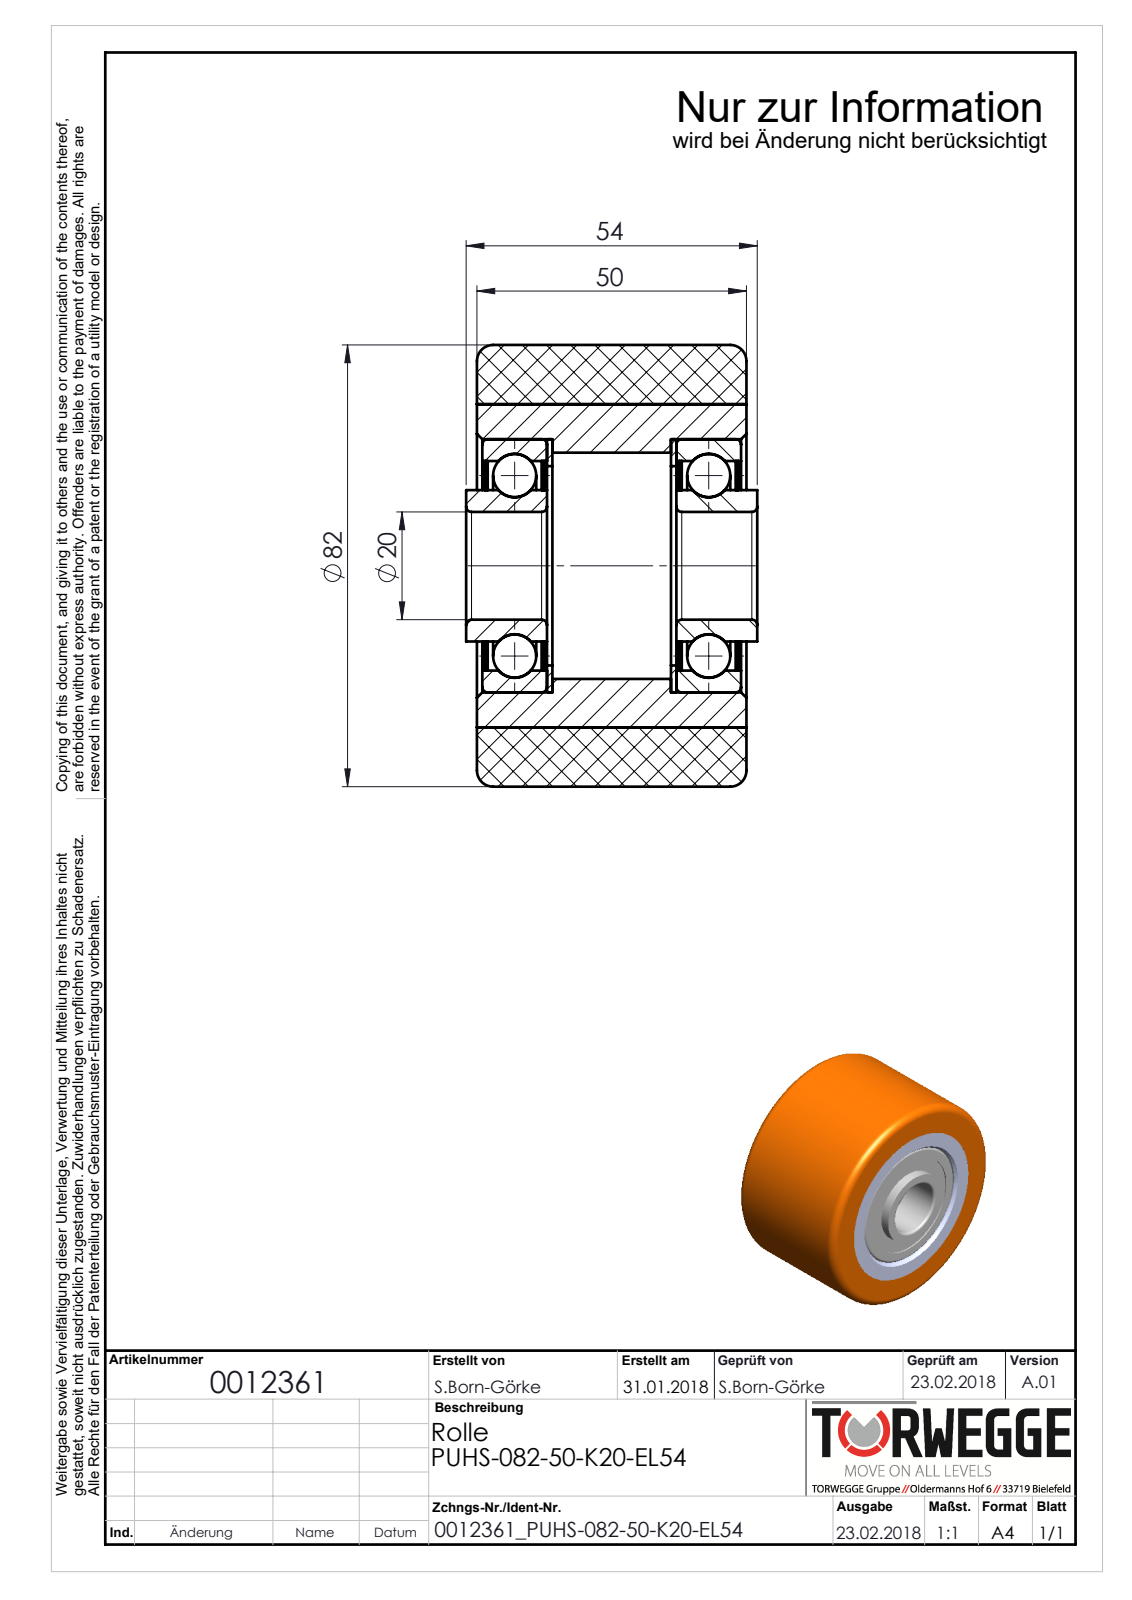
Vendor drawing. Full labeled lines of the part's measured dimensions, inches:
Part name (STEP PRODUCT): 0012361_PUHS-082-50-K20-EL54
STEP written by: SolidWorks 2016 (AUTOMOTIVE_DESIGN)
Units: inches
Bodies: 0 solids, 54 faces (10 planar, 24 cylindrical, 20 other)
Overall size (bounding box): 3.228 × 3.228 × 2.126
Round holes (diameter × count): ⌀0.787 ×1, ⌀1.531 ×1, ⌀1.654 ×1, ⌀1.85 ×1, ⌀2.362 ×1
Round bosses / shafts (diameter × count): ⌀3.228 ×1, ⌀1.106 ×1
Main face-to-face distances: 1.969, 0.059, 1.909, 0.039, 1.929, 0.02, 1.87, 1.85, 0.079, 0.118
